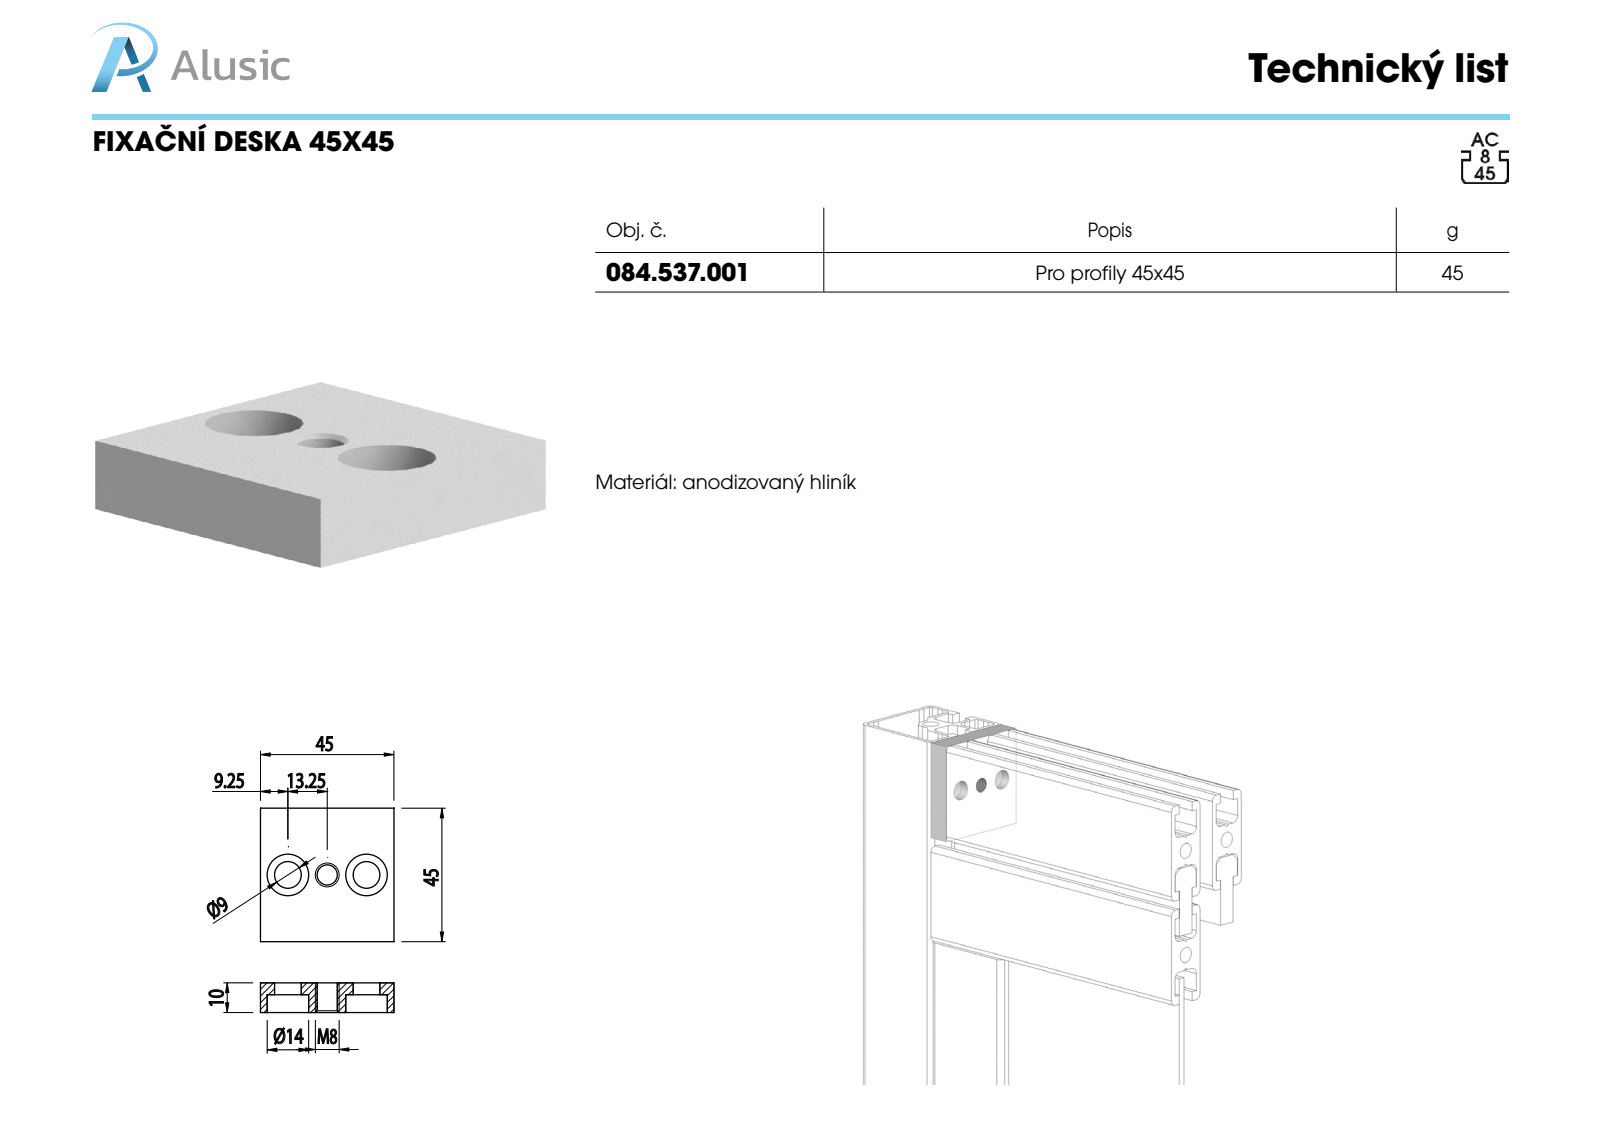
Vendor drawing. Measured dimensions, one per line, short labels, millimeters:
name: 084.537.001
written by: SolidWorks 2011 (CONFIG_CONTROL_DESIGN)
unit: mm
bodies: 1 solid, 20 faces (8 planar, 10 cylindrical, 2 other)
size: 45 × 45 × 10
volume: 17 526 mm³; area: 6 483 mm²
holes: 2× ⌀9, 2× ⌀14, 1× ⌀6.8
face distances: 10, 45, 4, 6
hole spacings: 13.25, 26.5
